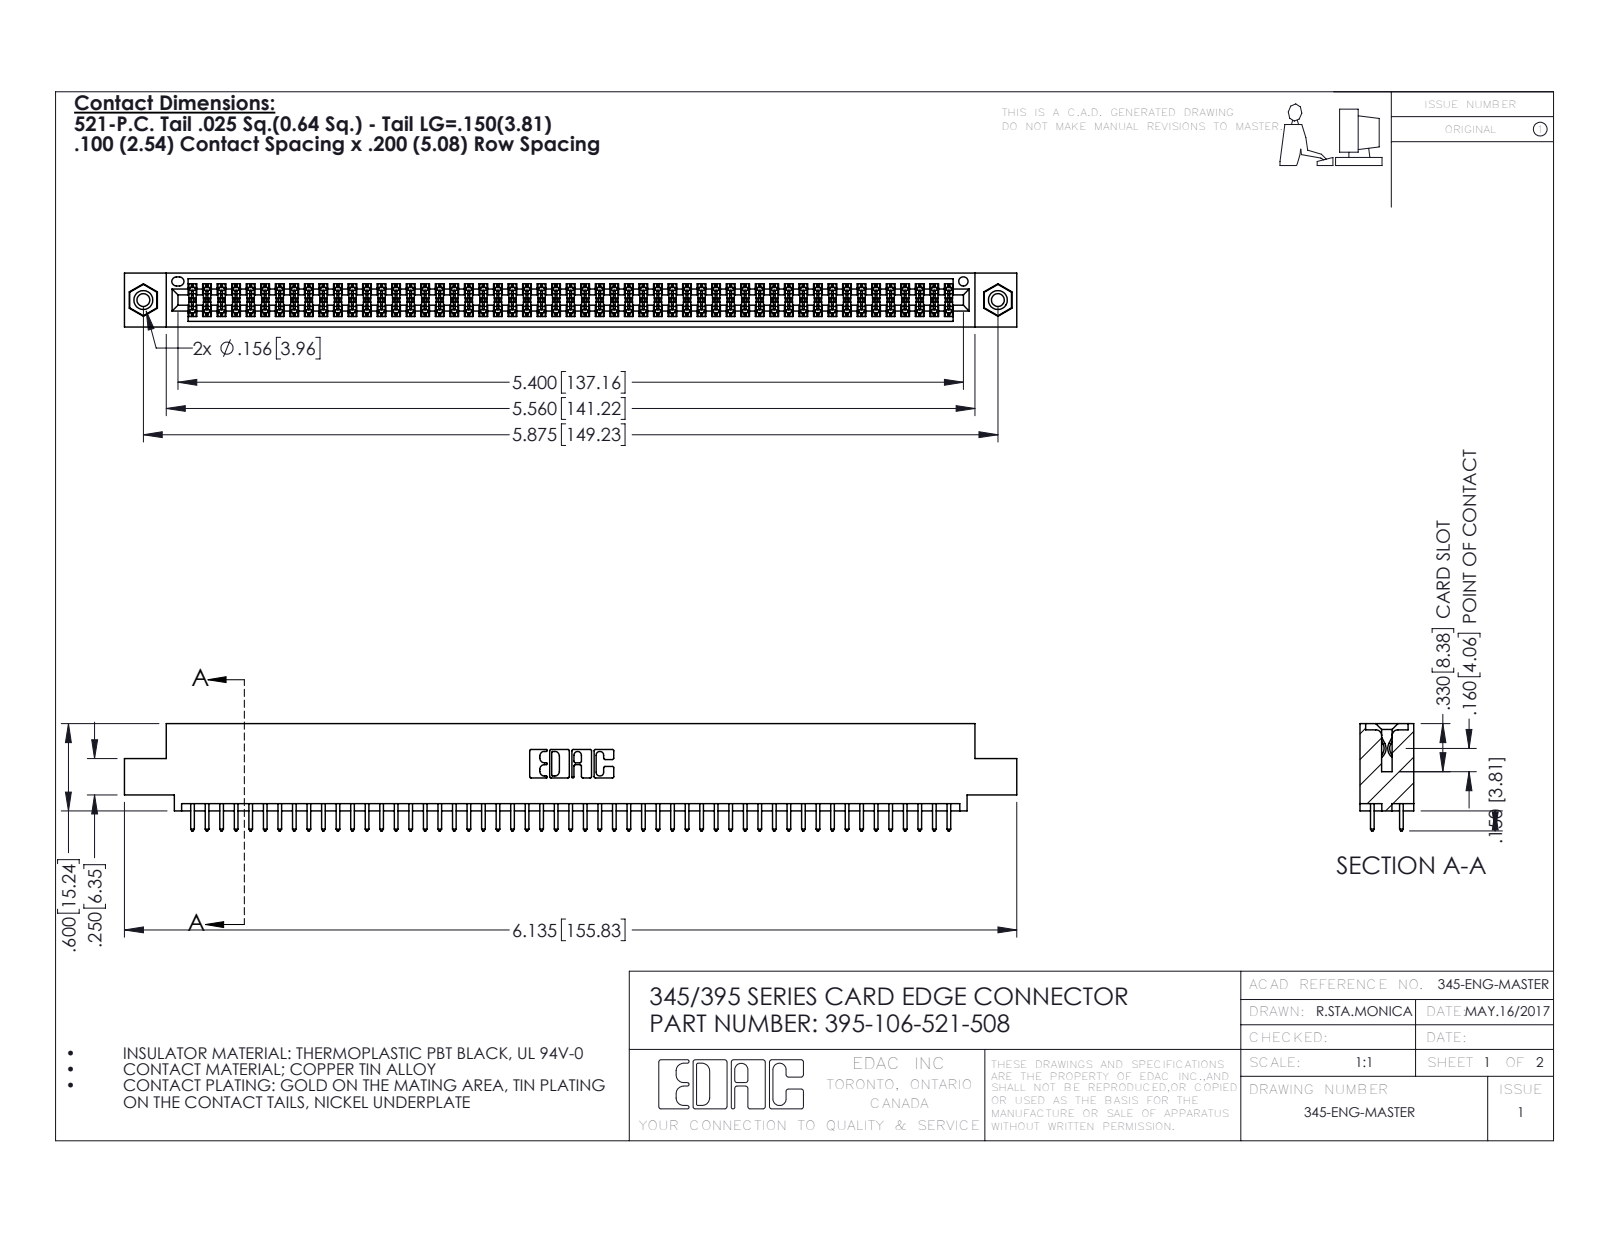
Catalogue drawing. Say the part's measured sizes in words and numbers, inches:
The part is named "395-106-521-508; 345-250-001_345-250-003-102; 345 Part_0.110 Offset - 0.156 Dia-TI; 345-292-001_345-293-121". Its 3-D file was written by "SolidWorks 2016 (CONFIG_CONTROL_DESIGN)". It is 109 solids with 5490 faces: 3614 planar, 1860 cylindrical and 16 other. Overall it measures 6.135 by 0.737 by 0.37 inches. Its volume is 0.922 cubic inches and its surface area 34.69 square inches. Round holes: 2 of diameter 0.089, 2 of diameter 0.125, 2 of diameter 0.156, 1 of diameter 0.064. Round bosses or shafts: 2 of diameter 0.155. Partial cylindrical surfaces (rounded edges, fillets, slot ends): 159 of radius 0.006, 106 of radius 0.01, 22 of radius 0.01, 6 of radius 0.007, 6 of radius 0.031, 3 of radius 0.026, 2 of radius 0.014, 2 of radius 0.019. The main face-to-face distances are 0.072, 0.298, 0.2, 0.098, 0.272, 0.025, 0.37, 0.225, 0.175, 0.149. The hole center spacings are 0.27, 5.639, 5.875.
